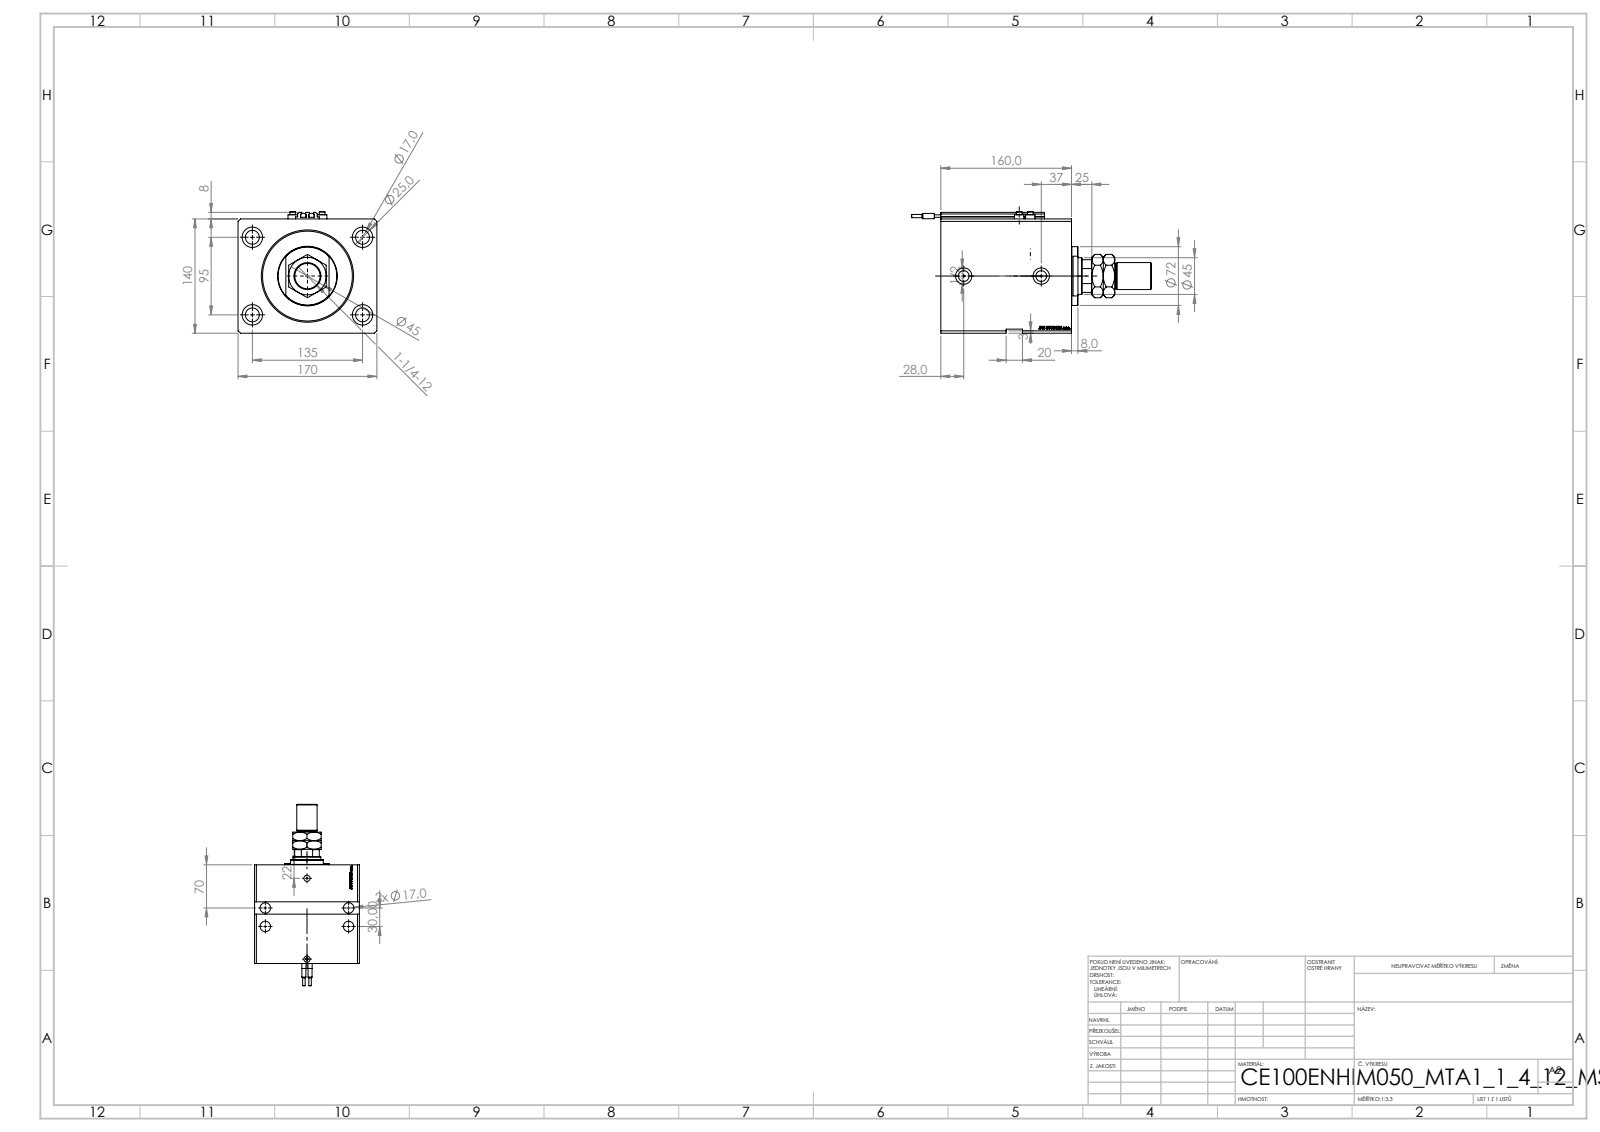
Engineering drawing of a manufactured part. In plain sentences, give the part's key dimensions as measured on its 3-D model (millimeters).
The part is named "V250CE_VC_E; V250CE_E_Body; MTA; SWITCH_V250CE (+2 more)". Its 3-D file was written by "SolidWorks 2019 (CONFIG_CONTROL_DESIGN)". It is 11 solids with 1224 faces: 594 planar, 154 cylindrical and 476 other. Overall it measures 294 by 170 by 149 millimeters. Its volume is 3 323 000 cubic millimeters and its surface area 359 413 square millimeters. Round holes: 8 of diameter 17, 4 of diameter 1.25, 4 of diameter 4, 4 of diameter 25, 2 of diameter 10, 2 of diameter 13.16, 2 of diameter 20, 1 of diameter 31.5, 1 of diameter 45, 1 of diameter 100, 1 of diameter 113. Round bosses or shafts: 4 of diameter 11.6, 4 of diameter 7, 2 of diameter 6.8, 2 of diameter 6.5, 2 of diameter 4, 1 of diameter 72, 1 of diameter 33, 1 of diameter 31. Partial cylindrical surfaces (rounded edges, fillets, slot ends): 10 of radius 0.2, 1 of radius 22. The main face-to-face distances are 140, 170, 160, 28.9, 131.1, 25, 135, 106.1, 50, 85. The hole center spacings are 82.54, 135, 95, 13.6, 30, 33.62, 36, 38.48.
